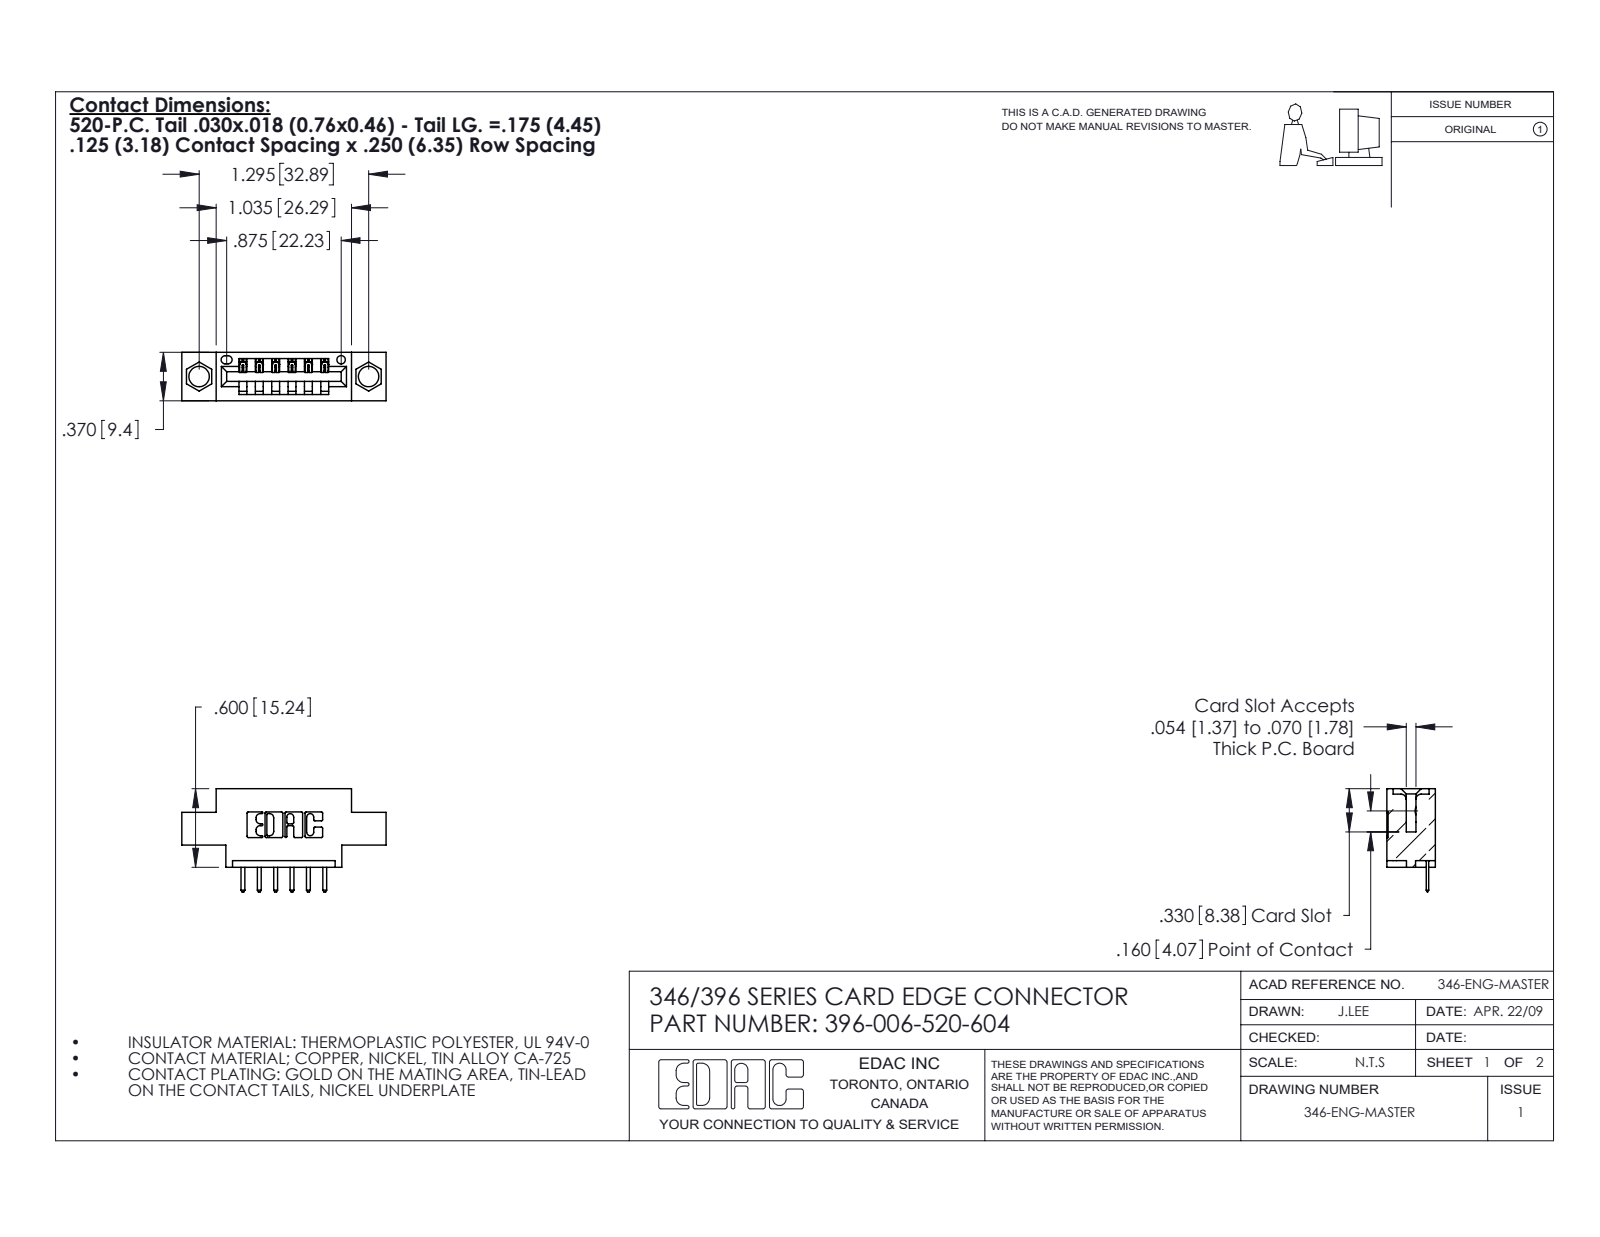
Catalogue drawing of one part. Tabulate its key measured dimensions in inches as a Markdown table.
| quantity | value |
| --- | --- |
| part name | 345-292-001_345-293-120; 396-006-520-604; 346 Part_0.170 Offset - 0.156 Dia-TH |
| STEP written by | SolidWorks 2020 (CONFIG_CONTROL_DESIGN) |
| units | inches |
| bodies | 7 solids, 512 faces (346 planar, 166 cylindrical, 0 other) |
| overall size | 1.56 × 0.788 × 0.37 |
| volume | 0.199 in³ |
| surface area | 5.634 in² |
| round holes (diameter × count) | 0.156 × 2, 0.064 × 1 |
| partial cylindrical surfaces (radius × count) | 0.01 × 22, 0.01 × 14, 0.006 × 12, 0.007 × 6, 0.031 × 6, 0.026 × 3, 0.031 × 2, 0.04 × 2 |
| main face-to-face distances | 0.25, 0.37, 0.048, 0.322, 0.222, 0.148, 0.1, 0.174, 0.125, 0.185 |
| hole center spacings | 0.246, 1.092, 1.295 |
